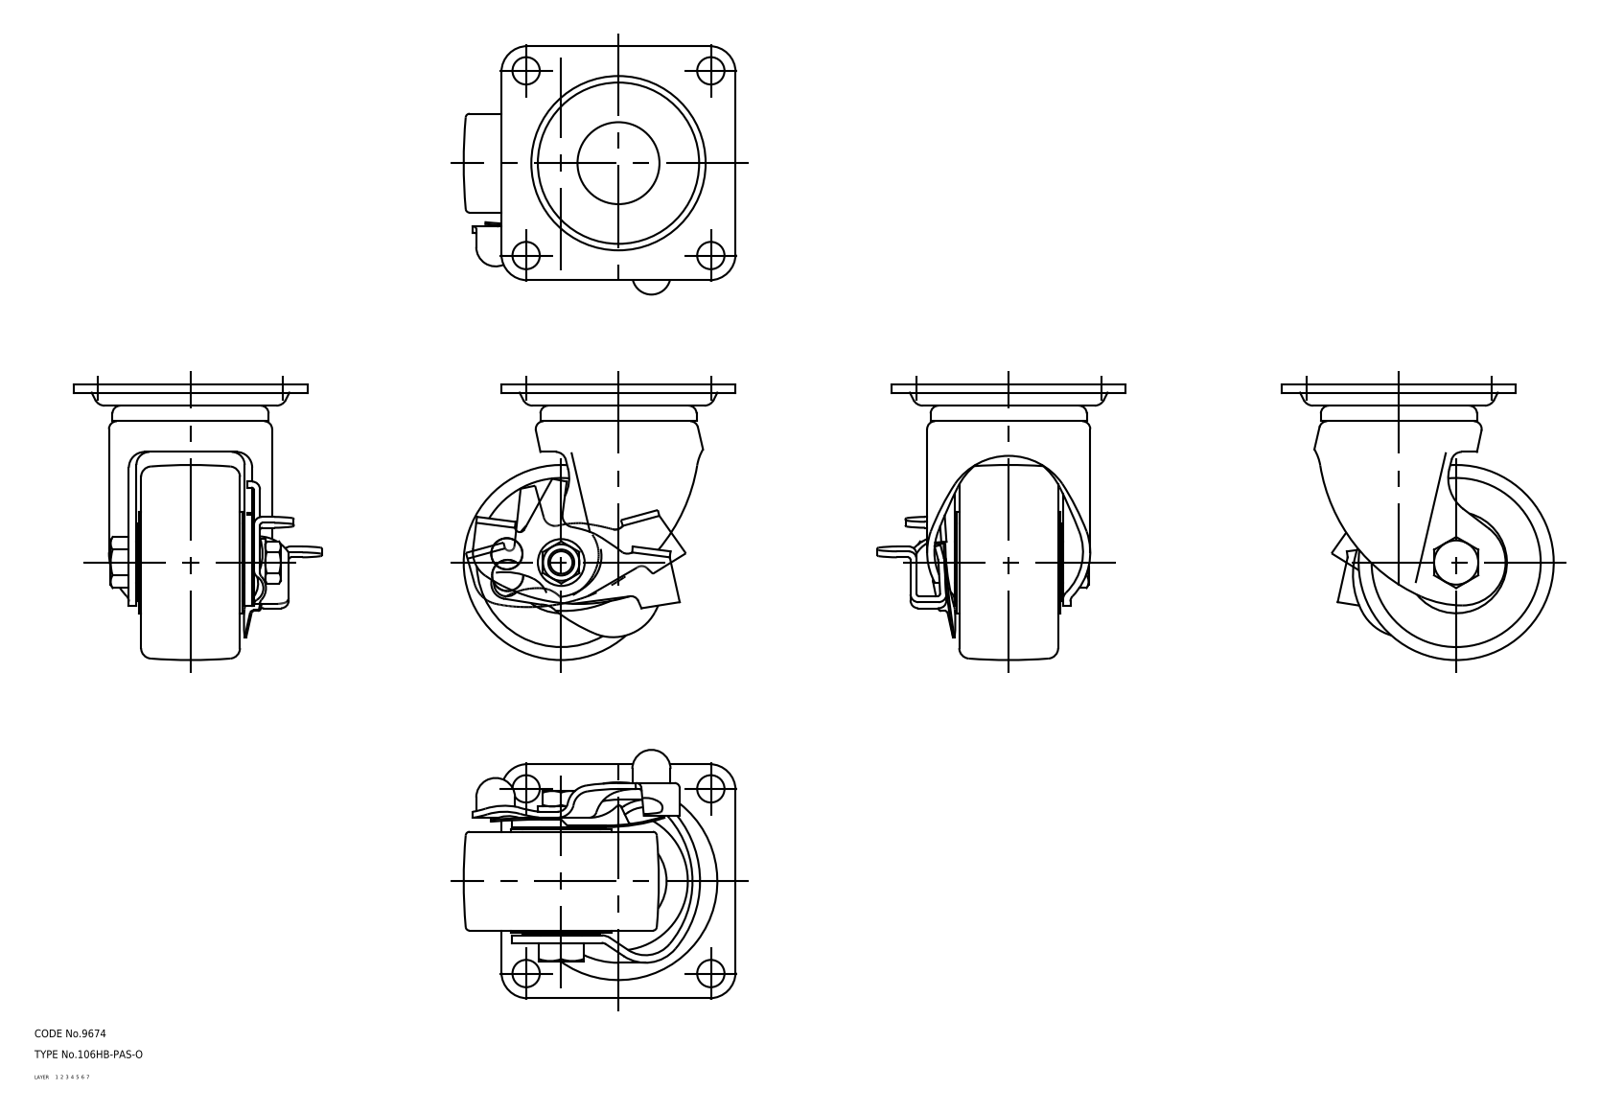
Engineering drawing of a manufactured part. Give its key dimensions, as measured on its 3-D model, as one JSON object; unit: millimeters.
{"part_name": "67134656; 67134669; 67134682; 67134695 (+8 more)", "step_written_by": "CADfix (AUTOMOTIVE_DESIGN)", "units": "millimeters", "bodies": {"solids": 6, "faces": 398, "planar": 0, "cylindrical": 0, "other": 398}, "overall_size": [106, 104.5, 95.5], "volume_mm3": 272672, "surface_area_mm2": 79515}
